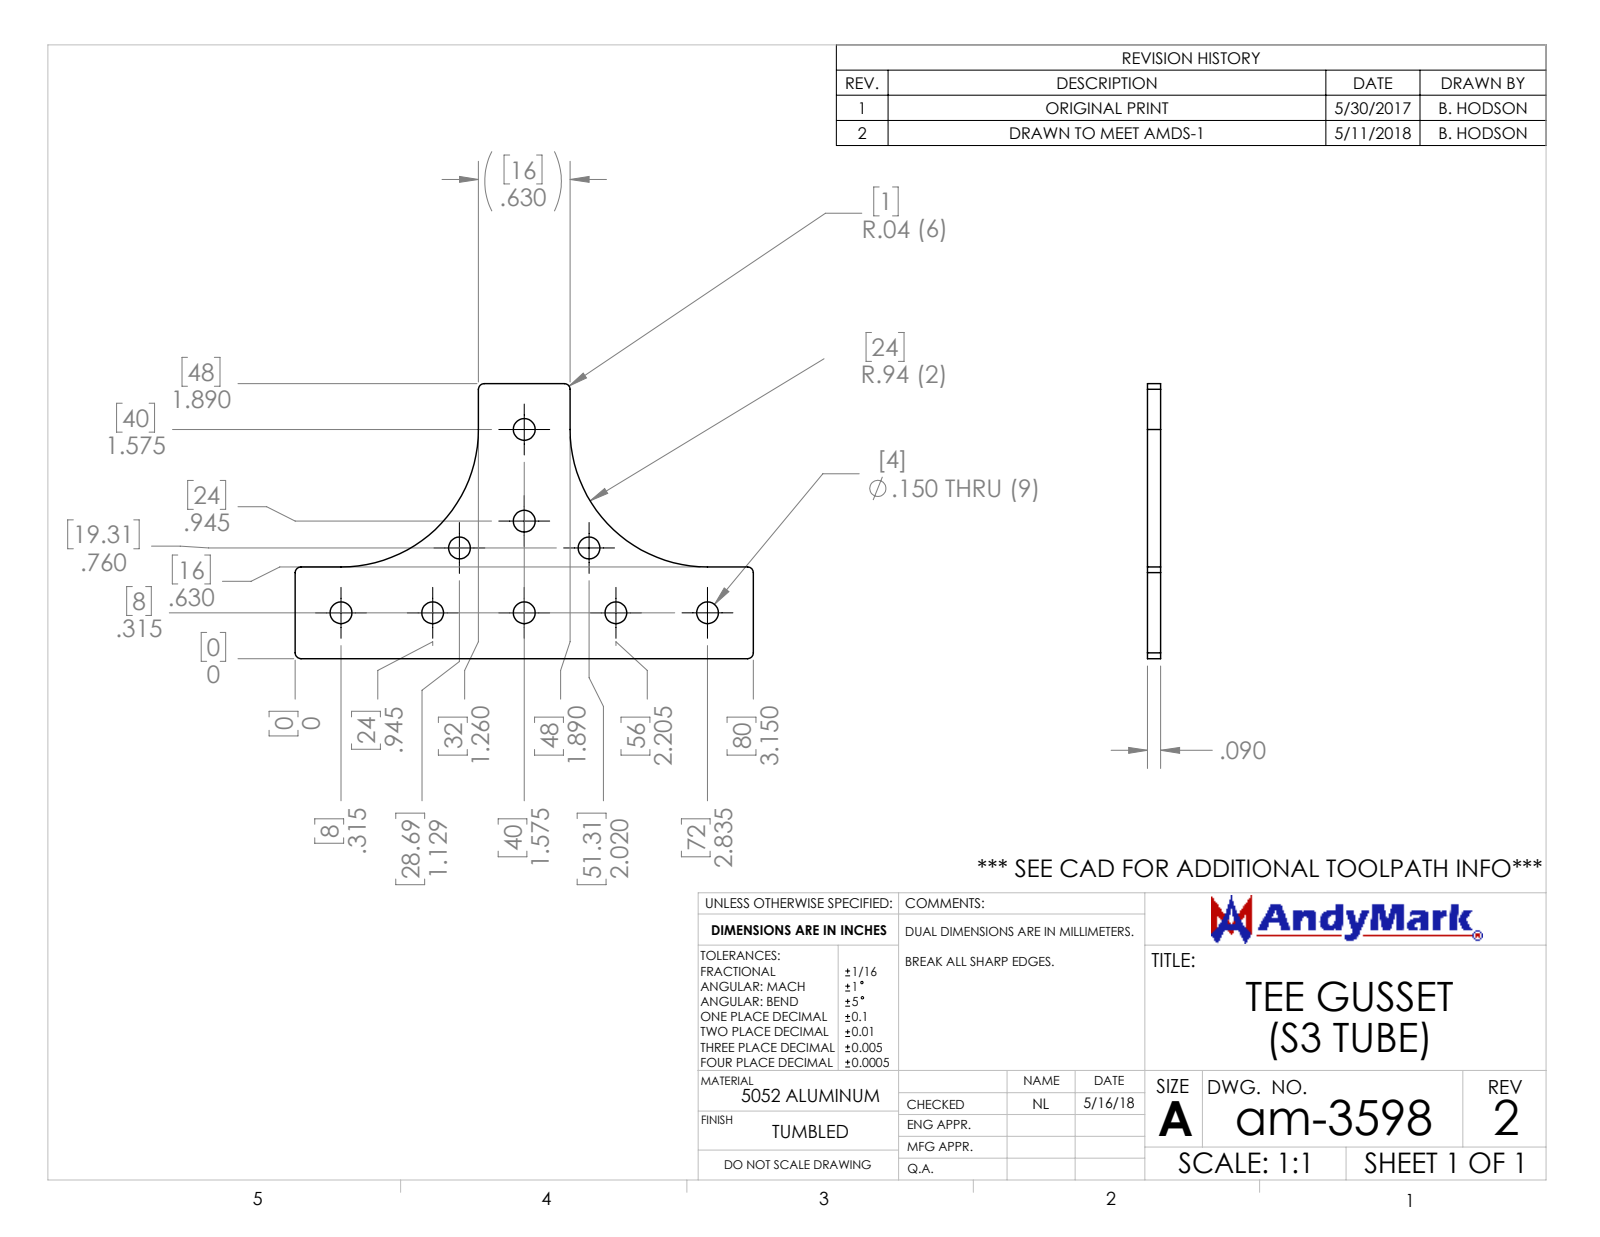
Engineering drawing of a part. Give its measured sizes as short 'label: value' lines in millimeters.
name: am-3598 Tee Gusset (S3 Tube) REV2
written by: SolidWorks 2017 (AUTOMOTIVE_DESIGN)
unit: mm
bodies: 1 solid, 36 faces (10 planar, 26 cylindrical, 0 other)
size: 80 × 48 × 2.29
volume: 4 424 mm³; area: 4 649 mm²
holes: 9× ⌀3.81
rounds: 6× R1, 2× R24
face distances: 2.29, 32, 48, 16, 80
hole spacings: 16, 12.24, 23.58, 32, 35.78, 15.99, 22.63, 29.56
